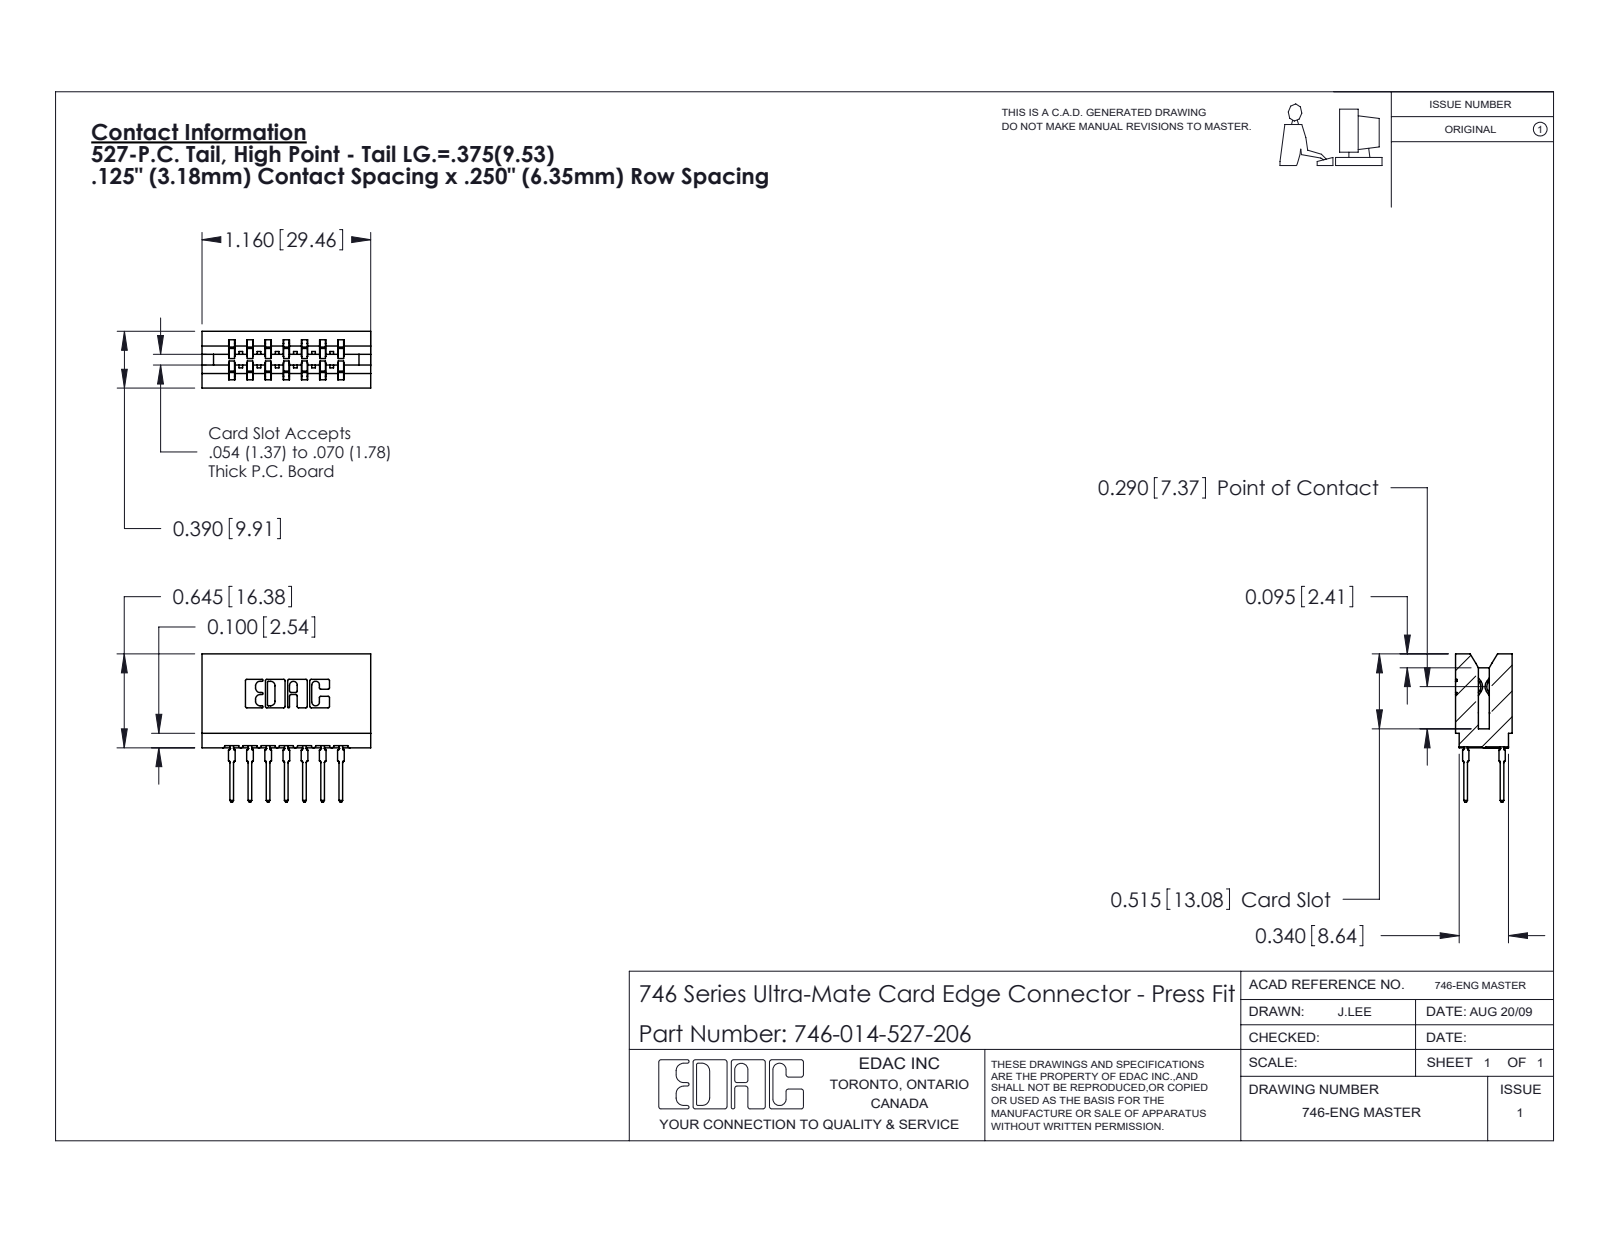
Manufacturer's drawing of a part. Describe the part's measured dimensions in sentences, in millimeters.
The part is named "746 Part_.515 Slot Depth - 06; 746-292-001_527; 746-014-527-206". Its 3-D file was written by "SolidWorks 2020 (CONFIG_CONTROL_DESIGN)". It is 15 solids with 1351 faces: 700 planar, 287 cylindrical and 364 other. Overall it measures 29.5 by 25.9 by 9.9 millimeters. Its volume is 3 380 cubic millimeters and its surface area 4 859 square millimeters. Partial cylindrical surfaces (rounded edges, fillets, slot ends): 28 of radius 0.5, 22 of radius 0.3, 8 of radius 0.1, 8 of radius 0.3, 8 of radius 0.4, 6 of radius 0.2, 6 of radius 0.8, 3 of radius 0.7. The main face-to-face distances are 6.4, 8.5, 1.4, 1.1, 3.2, 12.7, 3.2, 2.1, 5.3, 7.4.
